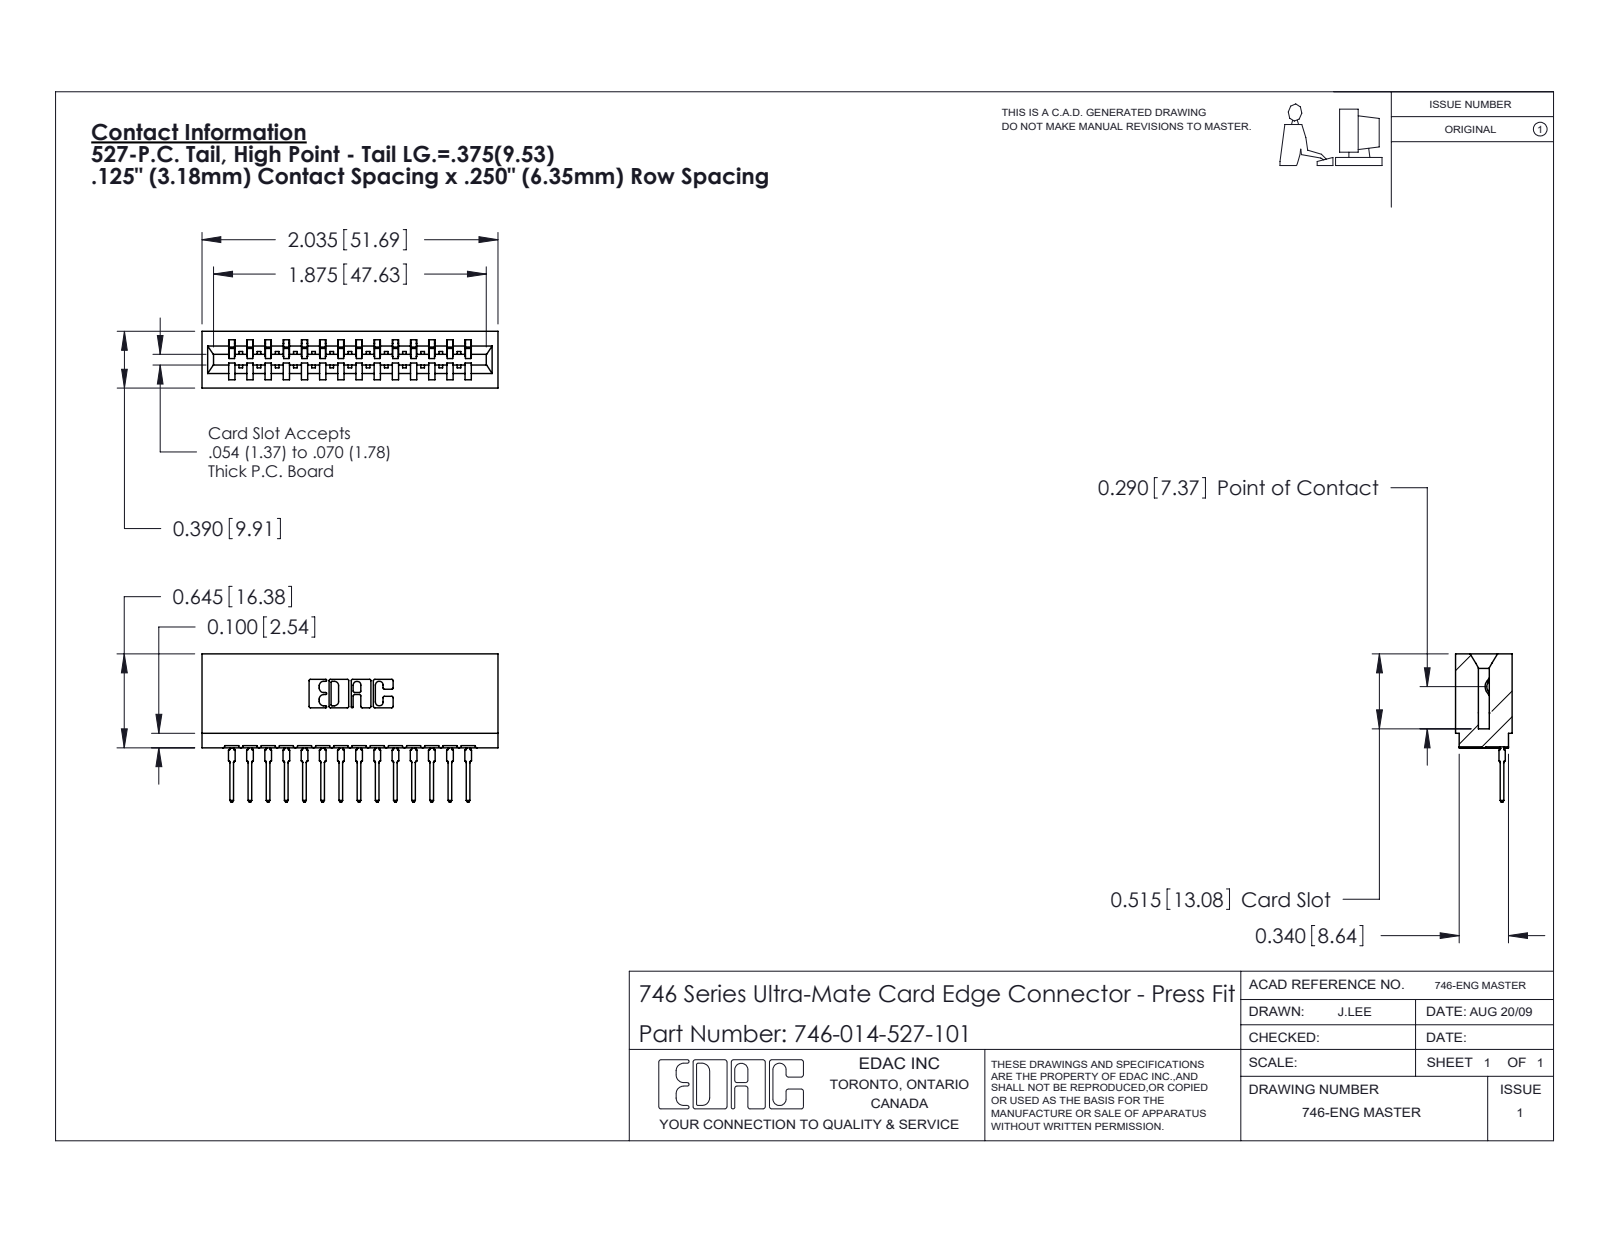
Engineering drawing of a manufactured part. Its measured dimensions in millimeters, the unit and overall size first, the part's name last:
Units: millimetres
Overall size (bounding box): 51.7 × 25.9 × 9.9
Partial cylindrical surfaces — rounded edges, fillets, slot ends (radius × count): R0.5 ×28, R0.3 ×22, R0.4 ×15, R0.2 ×6, R0.8 ×6, R0.1 ×4, R0.3 ×4, R0.7 ×3
Main face-to-face distances: 6.4, 8.5, 1.4, 12.7, 9.9, 1.1, 3.2, 5.3, 3.2, 2.1
Volume: 5 600 mm³ · Surface area: 7 916 mm²
Bodies: 15 solids, 1609 faces (937 planar, 308 cylindrical, 364 other)
Part name (STEP PRODUCT): 746-014-527-101; 746-292-001_527; 746 Part_.515 Slot Depth - 01
STEP written by: SolidWorks 2020 (CONFIG_CONTROL_DESIGN)
